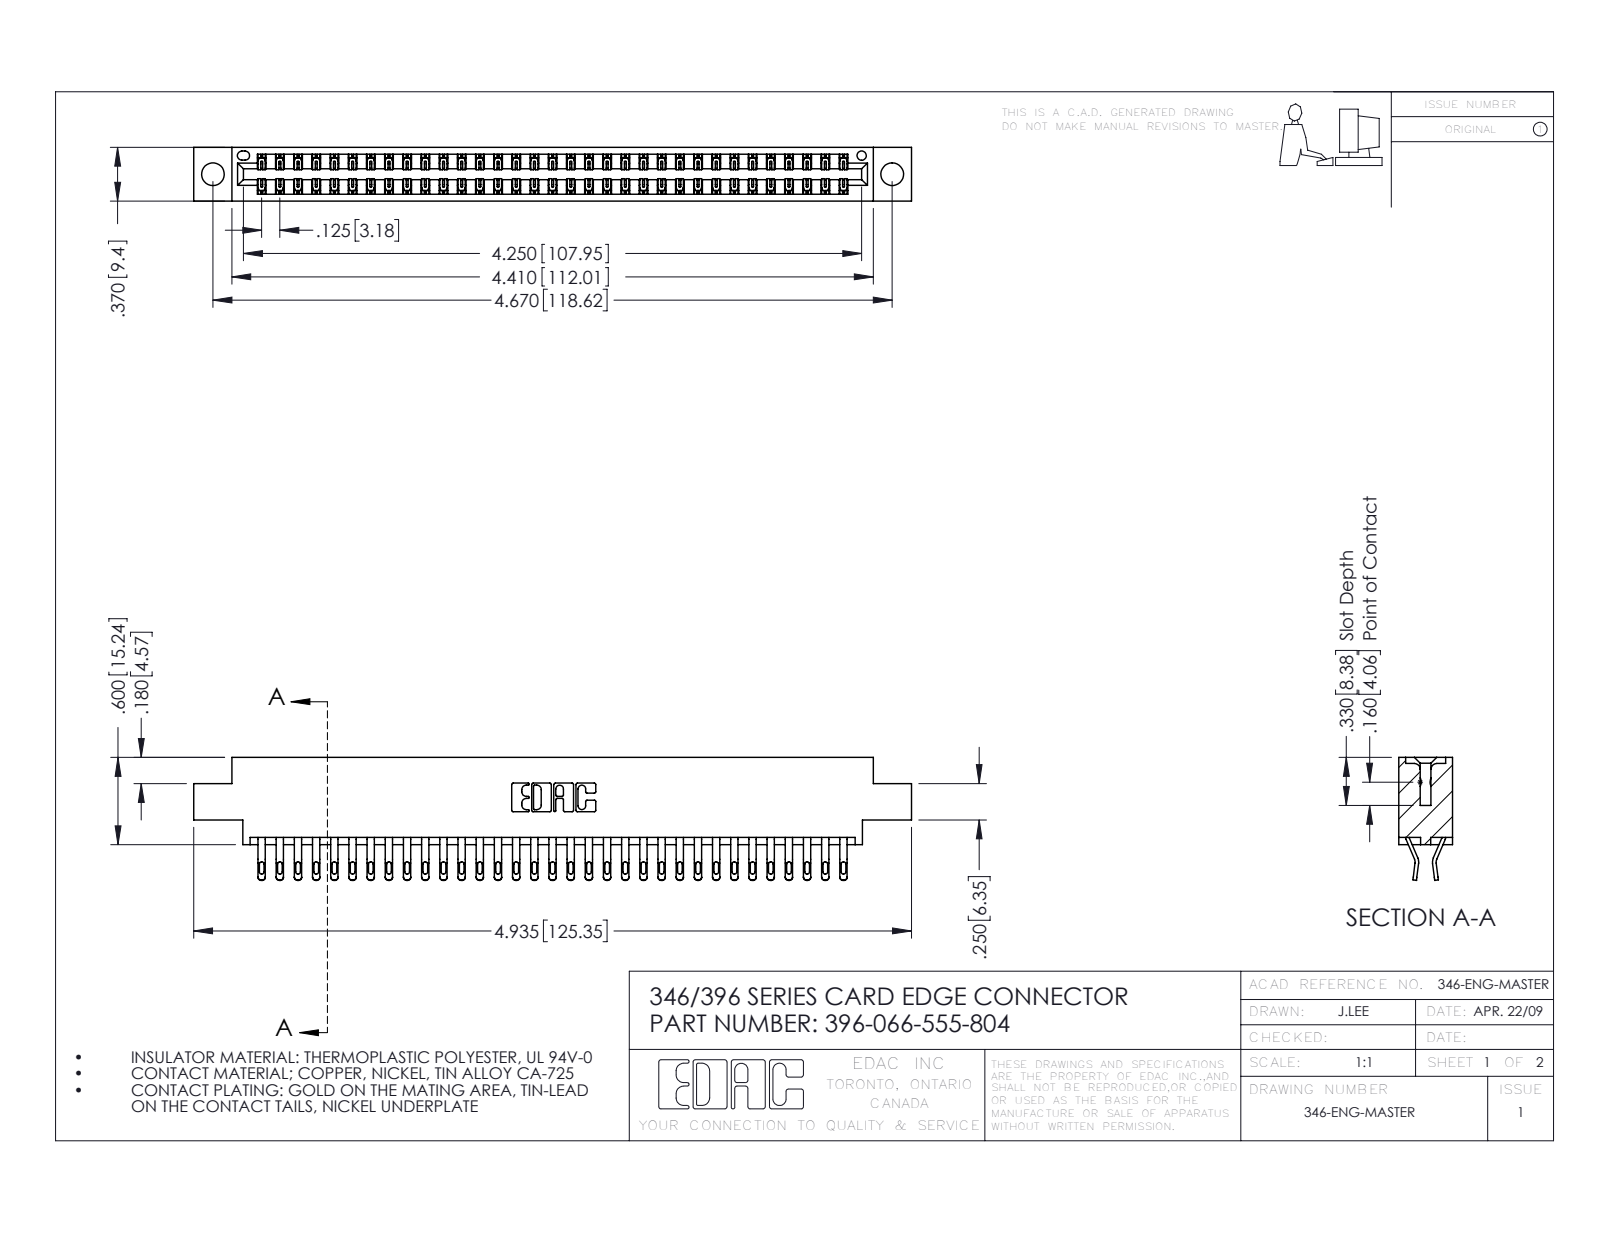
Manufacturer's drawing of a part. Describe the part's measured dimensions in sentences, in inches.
The part is named "345-292-001_555 Tail; 346 Part_0.170 Offset - 0.156 Dia-TH; 396-066-555-804". Its 3-D file was written by "SolidWorks 2016 (CONFIG_CONTROL_DESIGN)". It is 67 solids with 3954 faces: 2258 planar, 1696 cylindrical and 0 other. Overall it measures 4.935 by 0.845 by 0.37 inches. Its volume is 0.739 cubic inches and its surface area 26.61 square inches. Round holes: 2 of diameter 0.156, 1 of diameter 0.064. Partial cylindrical surfaces (rounded edges, fillets, slot ends): 132 of radius 0.016, 132 of radius 0.02, 99 of radius 0.006, 22 of radius 0.01, 6 of radius 0.007, 6 of radius 0.031, 3 of radius 0.026, 2 of radius 0.01. The main face-to-face distances are 0.048, 0.322, 0.37, 0.25, 0.025, 0.072, 0.298, 0.275, 0.148, 0.222. The hole center spacings are 0.246, 4.462, 4.67.
